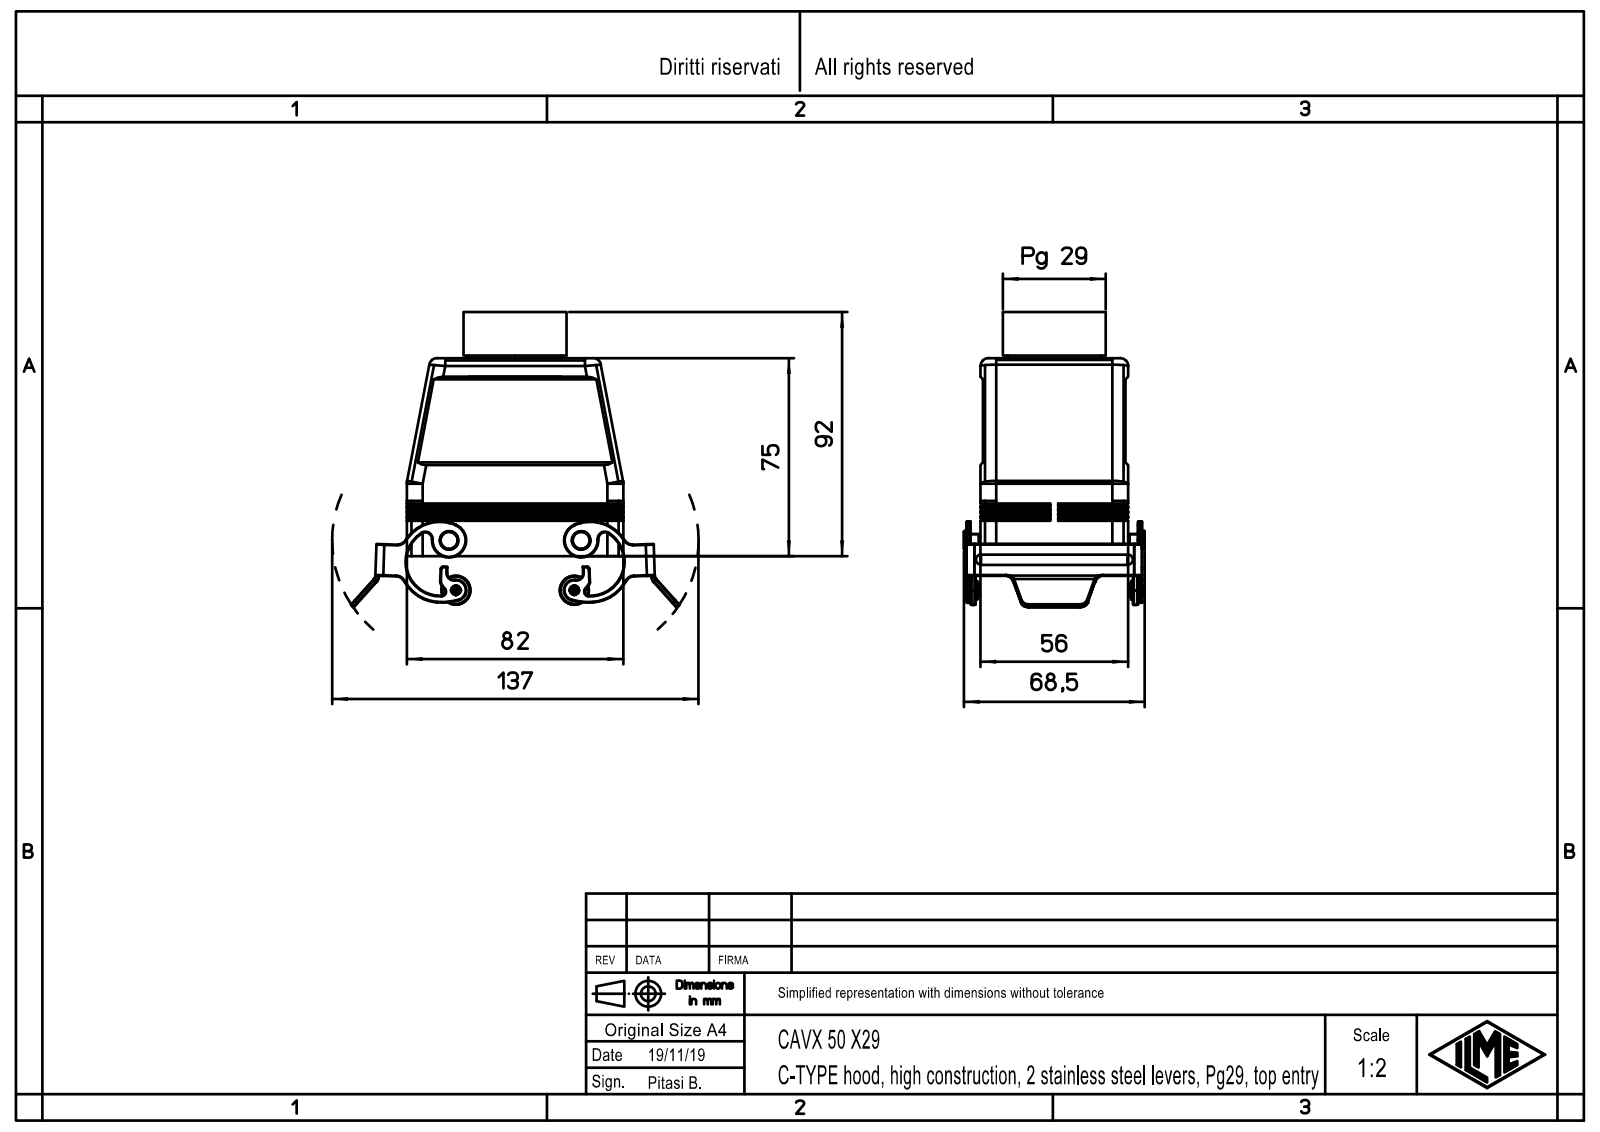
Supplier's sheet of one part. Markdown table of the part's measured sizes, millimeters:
| quantity | value |
| --- | --- |
| part name | Leva.1; Leva; CAVX 50 X29 |
| STEP written by | Creo Elements/Direct Modeling 20.1B 02-Apr-2019 (C) Parametric Technology GmbH (AUTOMOTIVE_DESIGN) |
| units | millimeters |
| bodies | 3 solids, 702 faces (280 planar, 326 cylindrical, 96 other) |
| overall size | 122.79 × 112.25 × 68.5 |
| volume | 88 205 mm³ |
| surface area | 61 448 mm² |
| round holes (diameter × count) | 2.46 × 8, 3.5 × 8, 5 × 4, 1.2 × 2, 2 × 2, 3.1 × 2, 32 × 1, 36.24 × 1 |
| round bosses / shafts (diameter × count) | 7 × 4, 4.8 × 4, 3 × 4, 11 × 2, 3.5 × 2, 40 × 1, 39 × 1, 35.3 × 1 |
| partial cylindrical surfaces (radius × count) | 3 × 20, 2 × 12, 6 × 10, 1.5 × 6, 3.5 × 6, 5.5 × 6, 2.5 × 4, 4 × 4 |
| main face-to-face distances | 3, 53, 1, 50, 2, 55, 52, 1.5, 8.25, 56 |
| hole center spacings | 16, 24, 33.24, 38.59, 66, 67.91, 70.23, 8 |
